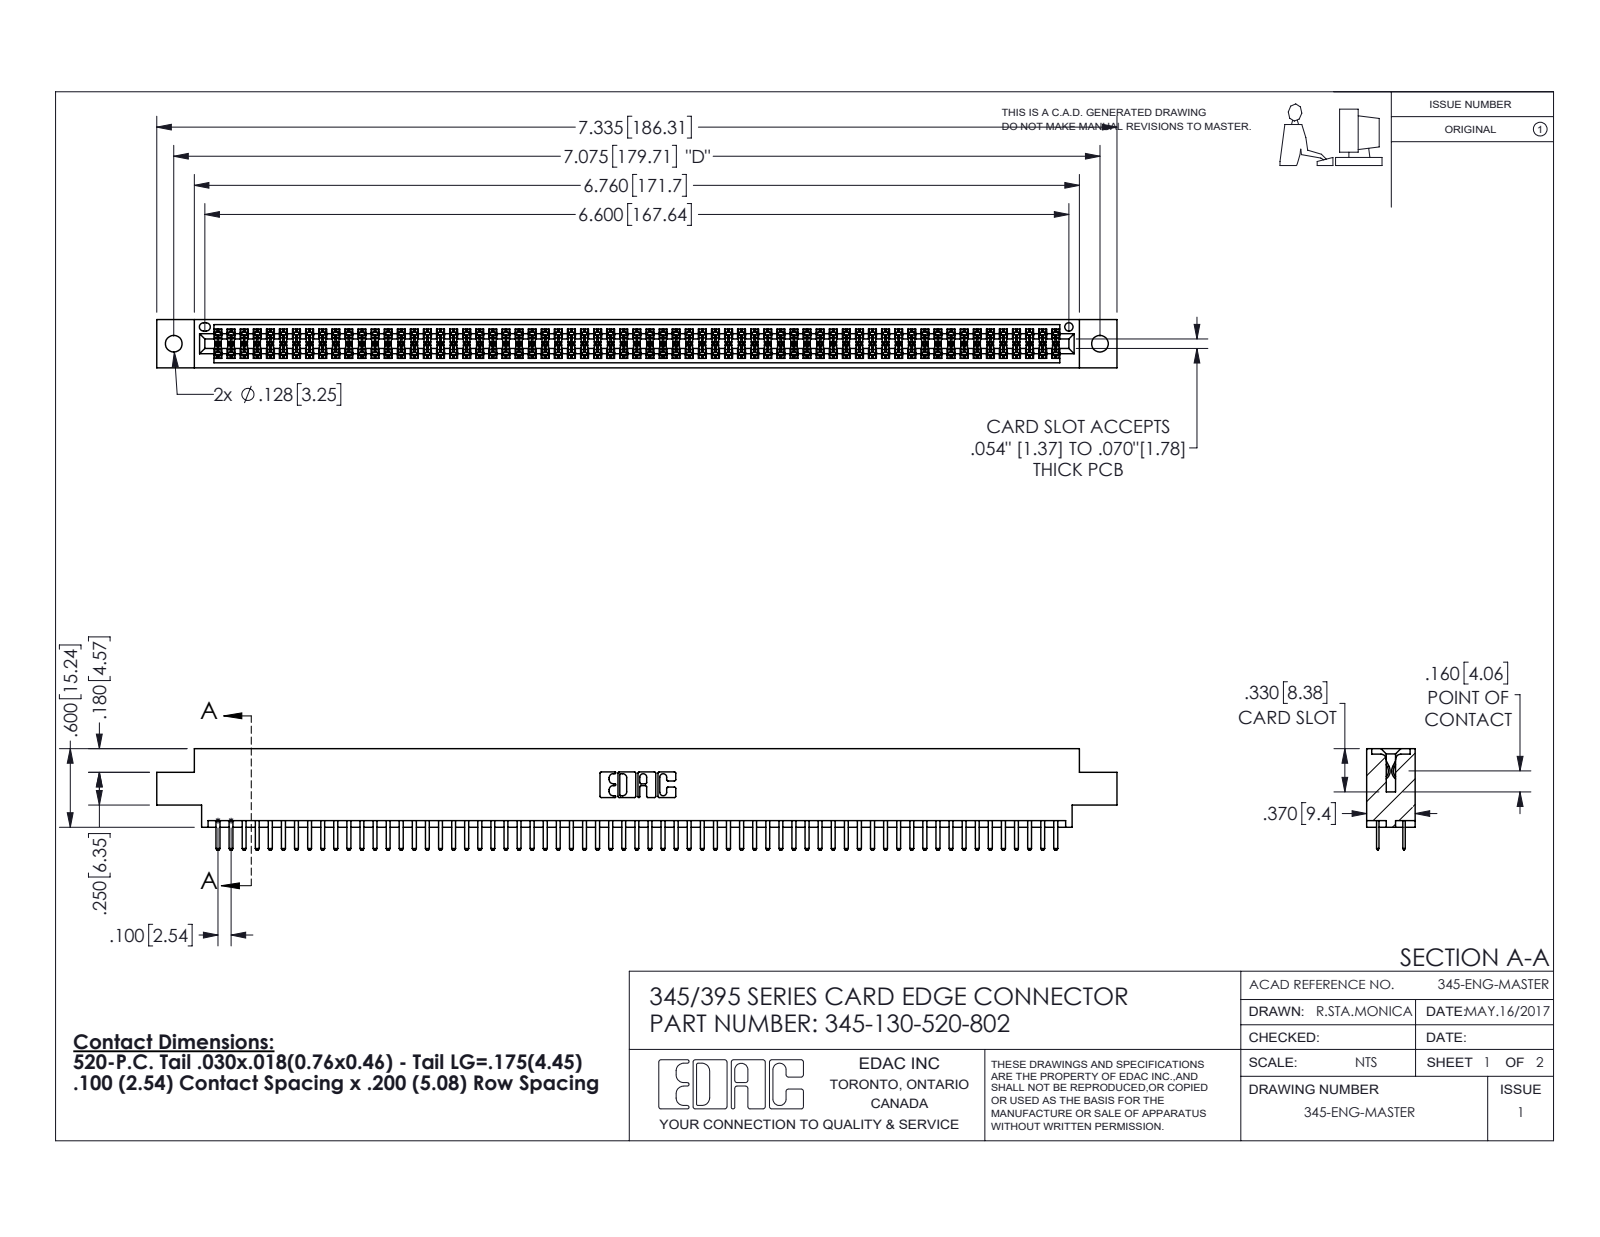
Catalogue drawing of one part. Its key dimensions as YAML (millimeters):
part_name: "345-292-001_345-293-120; 345-130-520-802; 345 Part_0.170 Offset - 0.128 Dia"
step_written_by: "SolidWorks 2016 (CONFIG_CONTROL_DESIGN)"
units: millimeters
bodies: {solids: 131, faces: 7150, planar: 4634, cylindrical: 2516, other: 0}
overall_size: [186.3, 19.7, 9.4]
volume: 18110
surface_area: 26950
round_holes:
  - {diameter: 3.3, count: 2}
  - {diameter: 1.6, count: 1}
partial_cylinders:
  - {radius: 0.2, count: 195}
  - {radius: 0.3, count: 134}
  - {radius: 0.3, count: 22}
  - {radius: 0.2, count: 6}
  - {radius: 0.8, count: 6}
  - {radius: 0.7, count: 3}
  - {radius: 0.4, count: 2}
  - {radius: 0.5, count: 2}
face_to_face_distances: [1.8, 7.6, 5.1, 9.4, 2.5, 6.9, 0.6, 5.7, 0.6, 1.8]
hole_center_spacings: [6.9, 173.7, 179.7]
